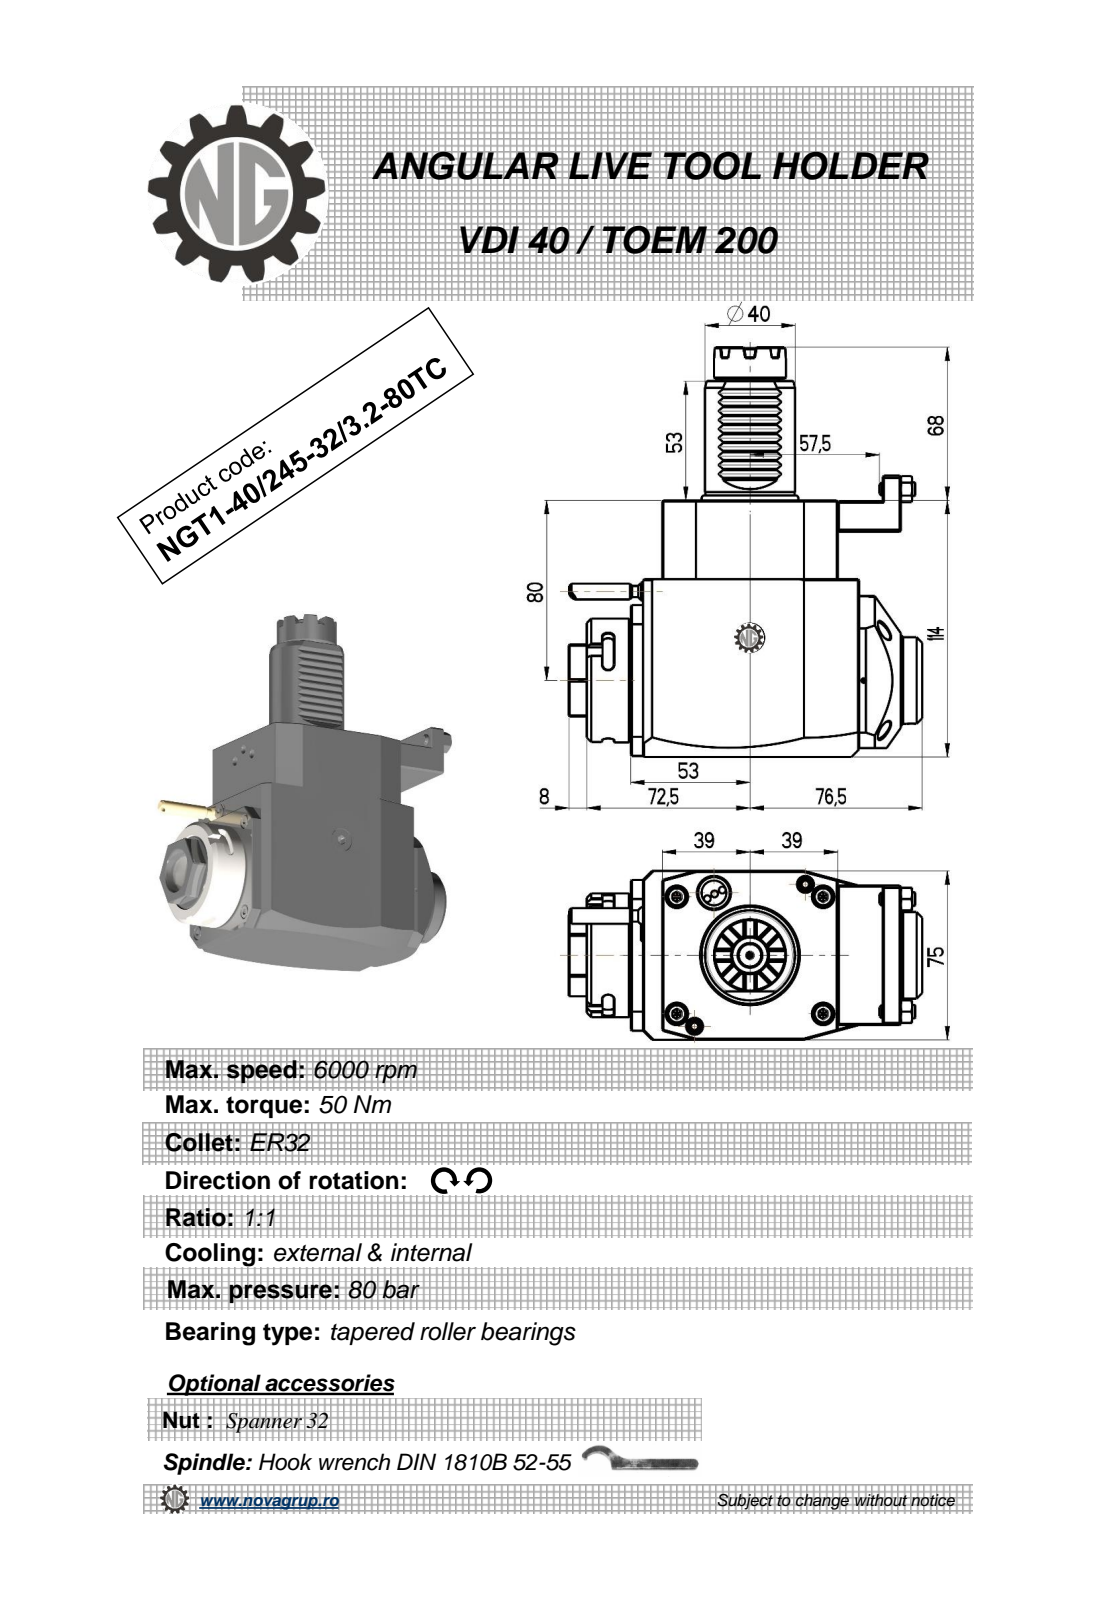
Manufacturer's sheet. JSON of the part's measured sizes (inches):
{"part_name": "NGT1_40_245_32_3_2_80TC", "step_written_by": "PRO/ENGINEER BY PARAMETRIC TECHNOLOGY CORPORATION, 2010280 (CONFIG_CONTROL_DESIGN)", "units": "inches", "bodies": {"solids": 1, "faces": 425, "planar": 225, "cylindrical": 68, "other": 132}, "overall_size": [7.165, 6.181, 2.953], "volume_in3": 60.59, "surface_area_in2": 118.6, "round_holes": [[0.098, 1], [0.118, 1], [0.906, 1]], "round_bosses_or_shafts": [[0.236, 2], [2.165, 1], [1.89, 1], [1.575, 1], [1.516, 1], [1.26, 1], [0.677, 1], [0.315, 1]], "partial_cylinders_radius": [[0.012, 10], [0.012, 10], [0.098, 6], [7.087, 2], [0.02, 1], [0.965, 1], [1.476, 1]], "face_to_face_distances": [2.953, 0.551, 4.488, 1.102, 0.02, 0.374, 5.492, 3.937, 0.768, 1.319], "hole_center_spacings": [1.701]}
